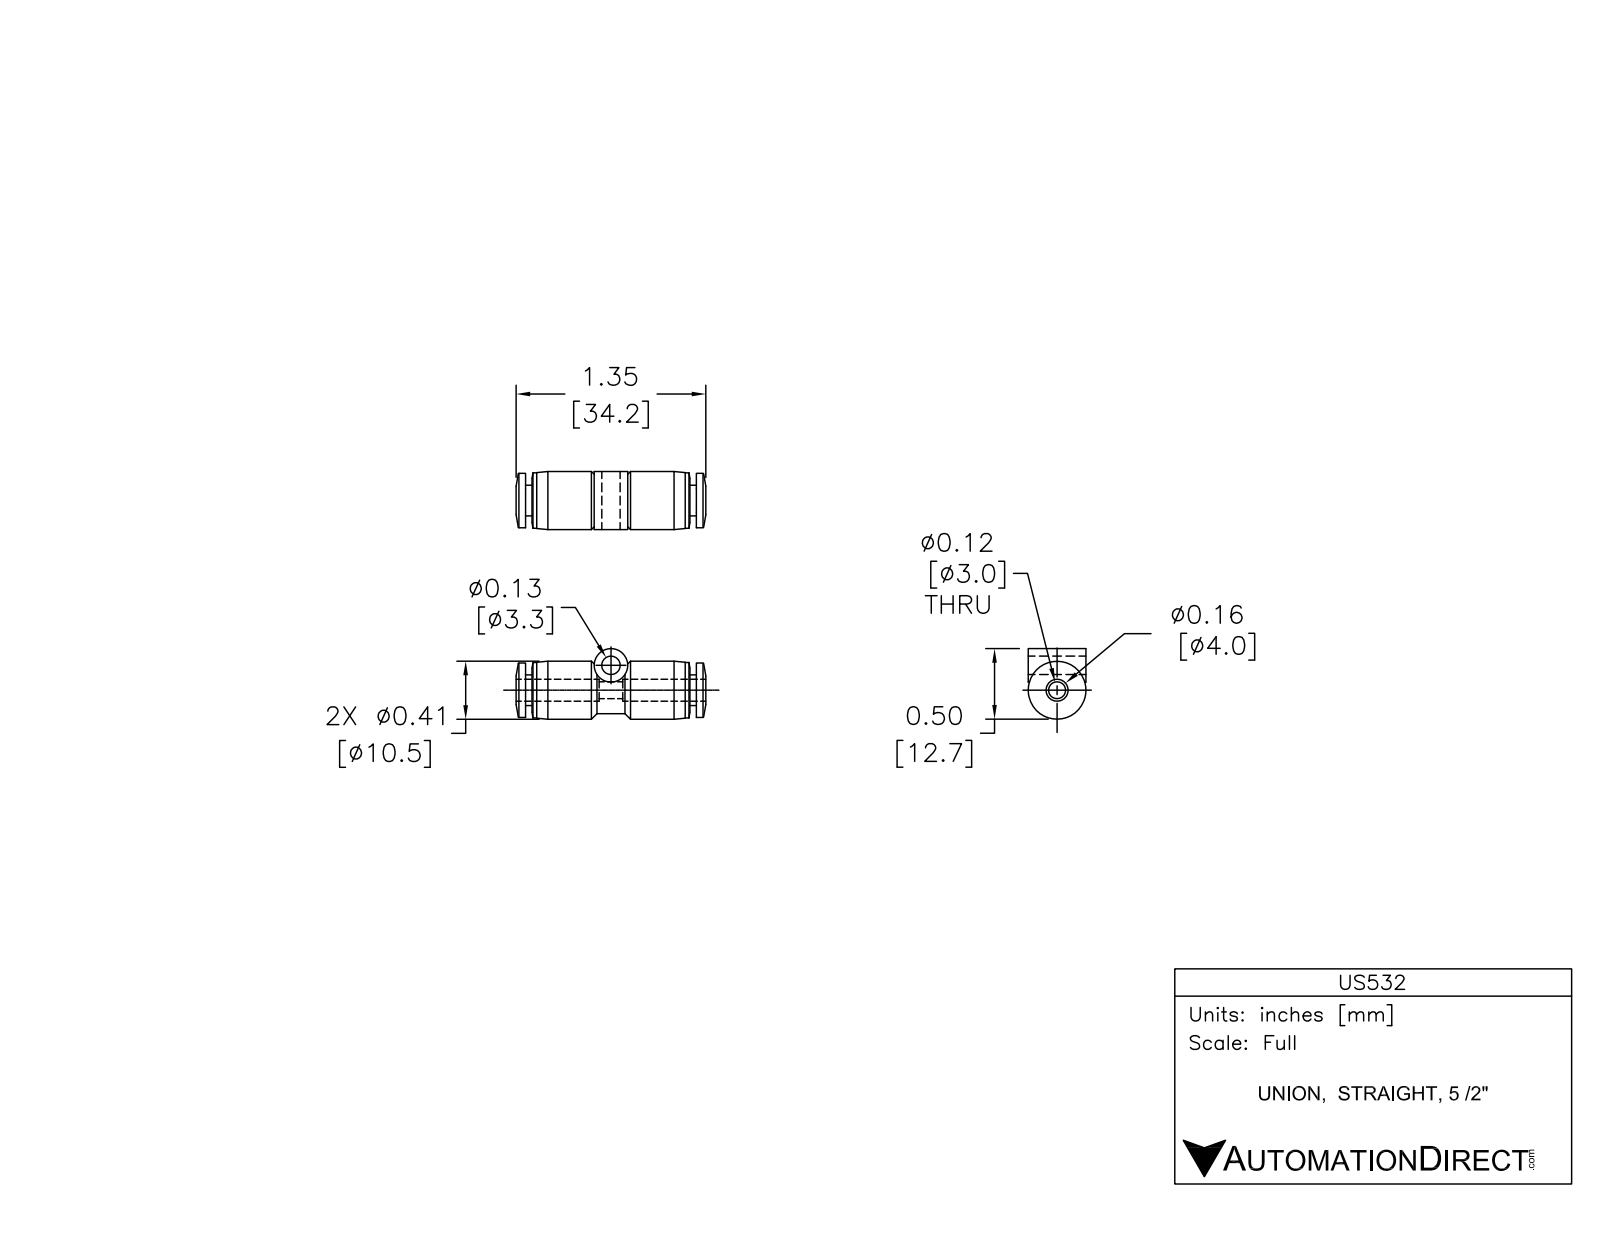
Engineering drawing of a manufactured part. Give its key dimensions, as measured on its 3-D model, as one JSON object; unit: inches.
{"part_name": "US532", "step_written_by": "SolidWorks 2015 (AUTOMOTIVE_DESIGN)", "units": "inches", "bodies": {"solids": 1, "faces": 66, "planar": 10, "cylindrical": 28, "other": 28}, "overall_size": [1.339, 0.502, 0.413], "volume_in3": 0.134, "surface_area_in2": 3.164, "round_holes": [[0.13, 1], [0.134, 1], [0.169, 1]], "round_bosses_or_shafts": [[0.413, 1], [0.394, 1], [0.388, 1], [0.236, 1], [0.22, 1]], "partial_cylinders_radius": [[0.167, 1]], "face_to_face_distances": [1.205, 0.045, 1.159, 1.114, 0.413, 0.516, 0.689, 0.47, 0.644, 0.173]}
